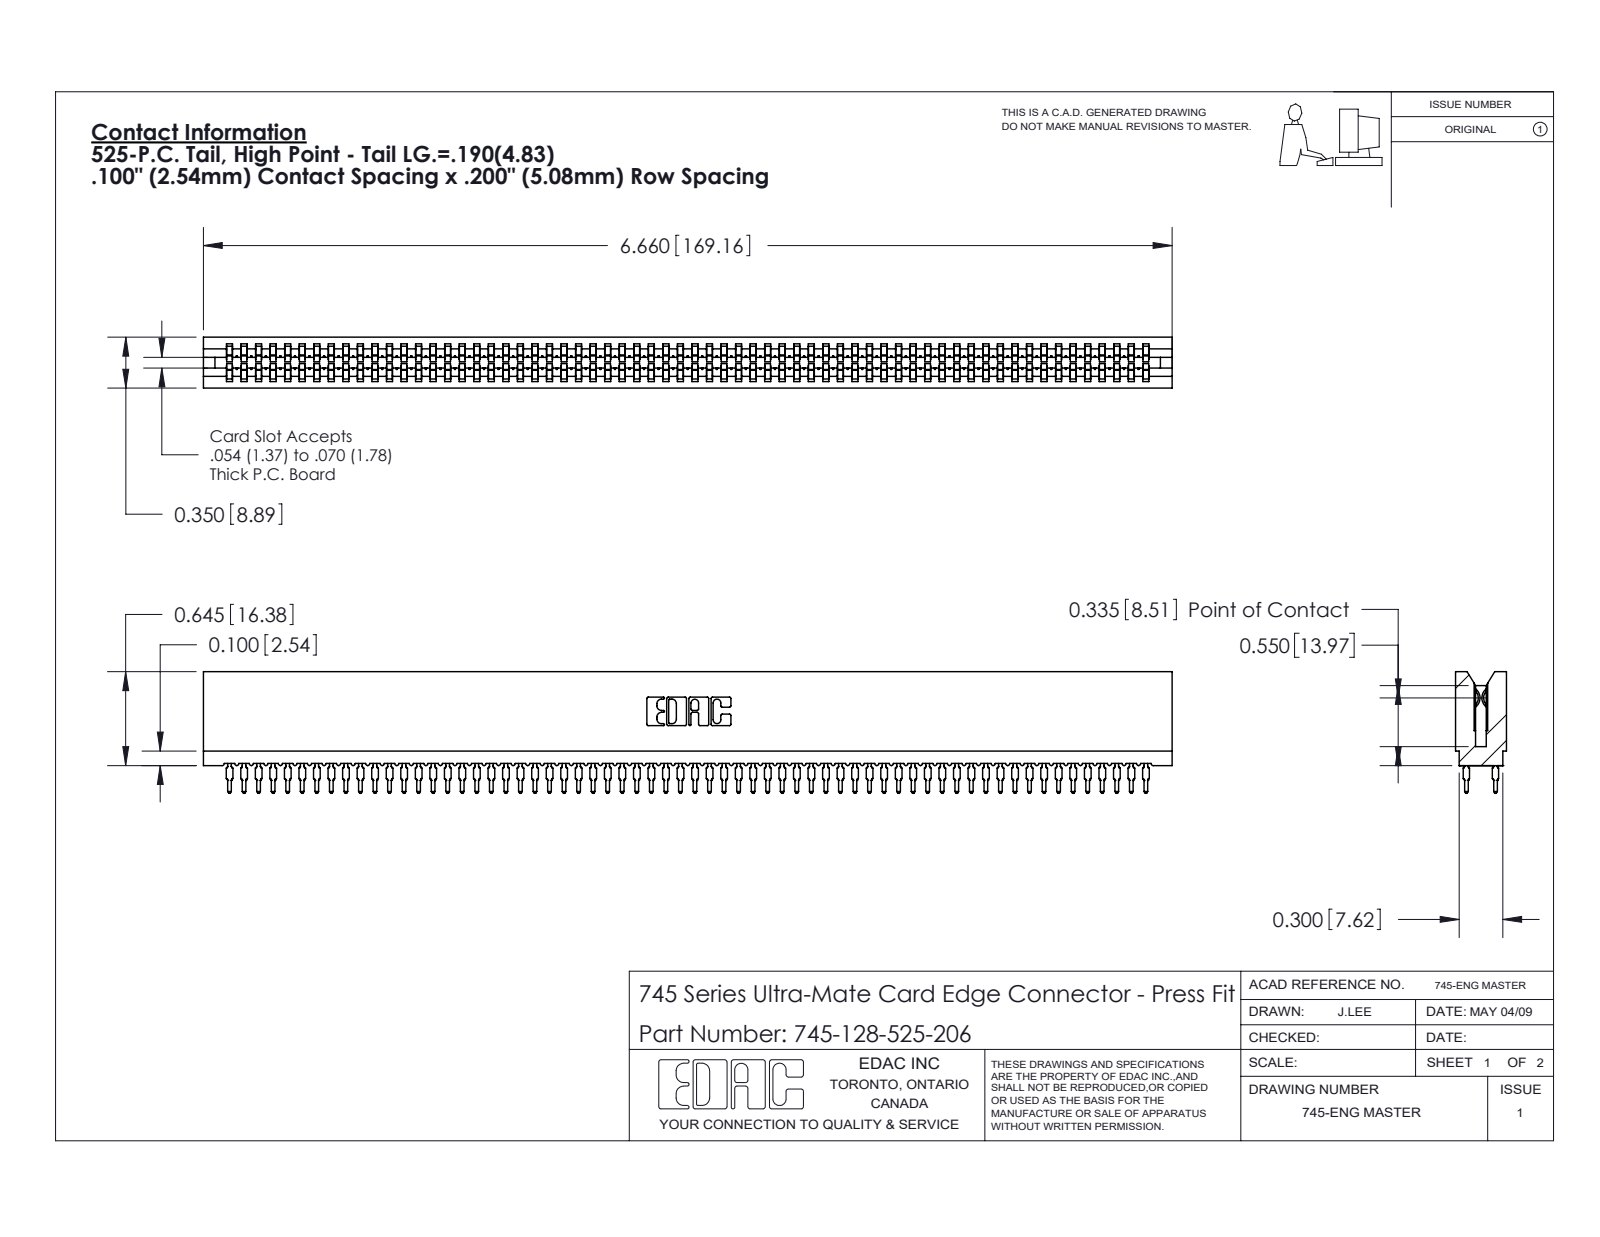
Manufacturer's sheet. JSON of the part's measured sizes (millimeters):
{"part_name": "745-128-525-206; 745 Part_Insulator Option - 06; 745-292-001_525", "step_written_by": "SolidWorks 2020 (CONFIG_CONTROL_DESIGN)", "units": "millimeters", "bodies": {"solids": 129, "faces": 11552, "planar": 5944, "cylindrical": 2280, "other": 3328}, "overall_size": [169.2, 21.2, 8.9], "volume_mm3": 15000, "surface_area_mm2": 31000, "partial_cylinders_radius": [[0.5, 256], [0.4, 128], [0.3, 22], [0.1, 8], [0.3, 8], [0.2, 6], [0.8, 6], [0.7, 3]], "face_to_face_distances": [8.9, 1.6, 7.3, 1.1, 7.7, 0.5, 6.2, 3.5, 5.4, 2.4]}
